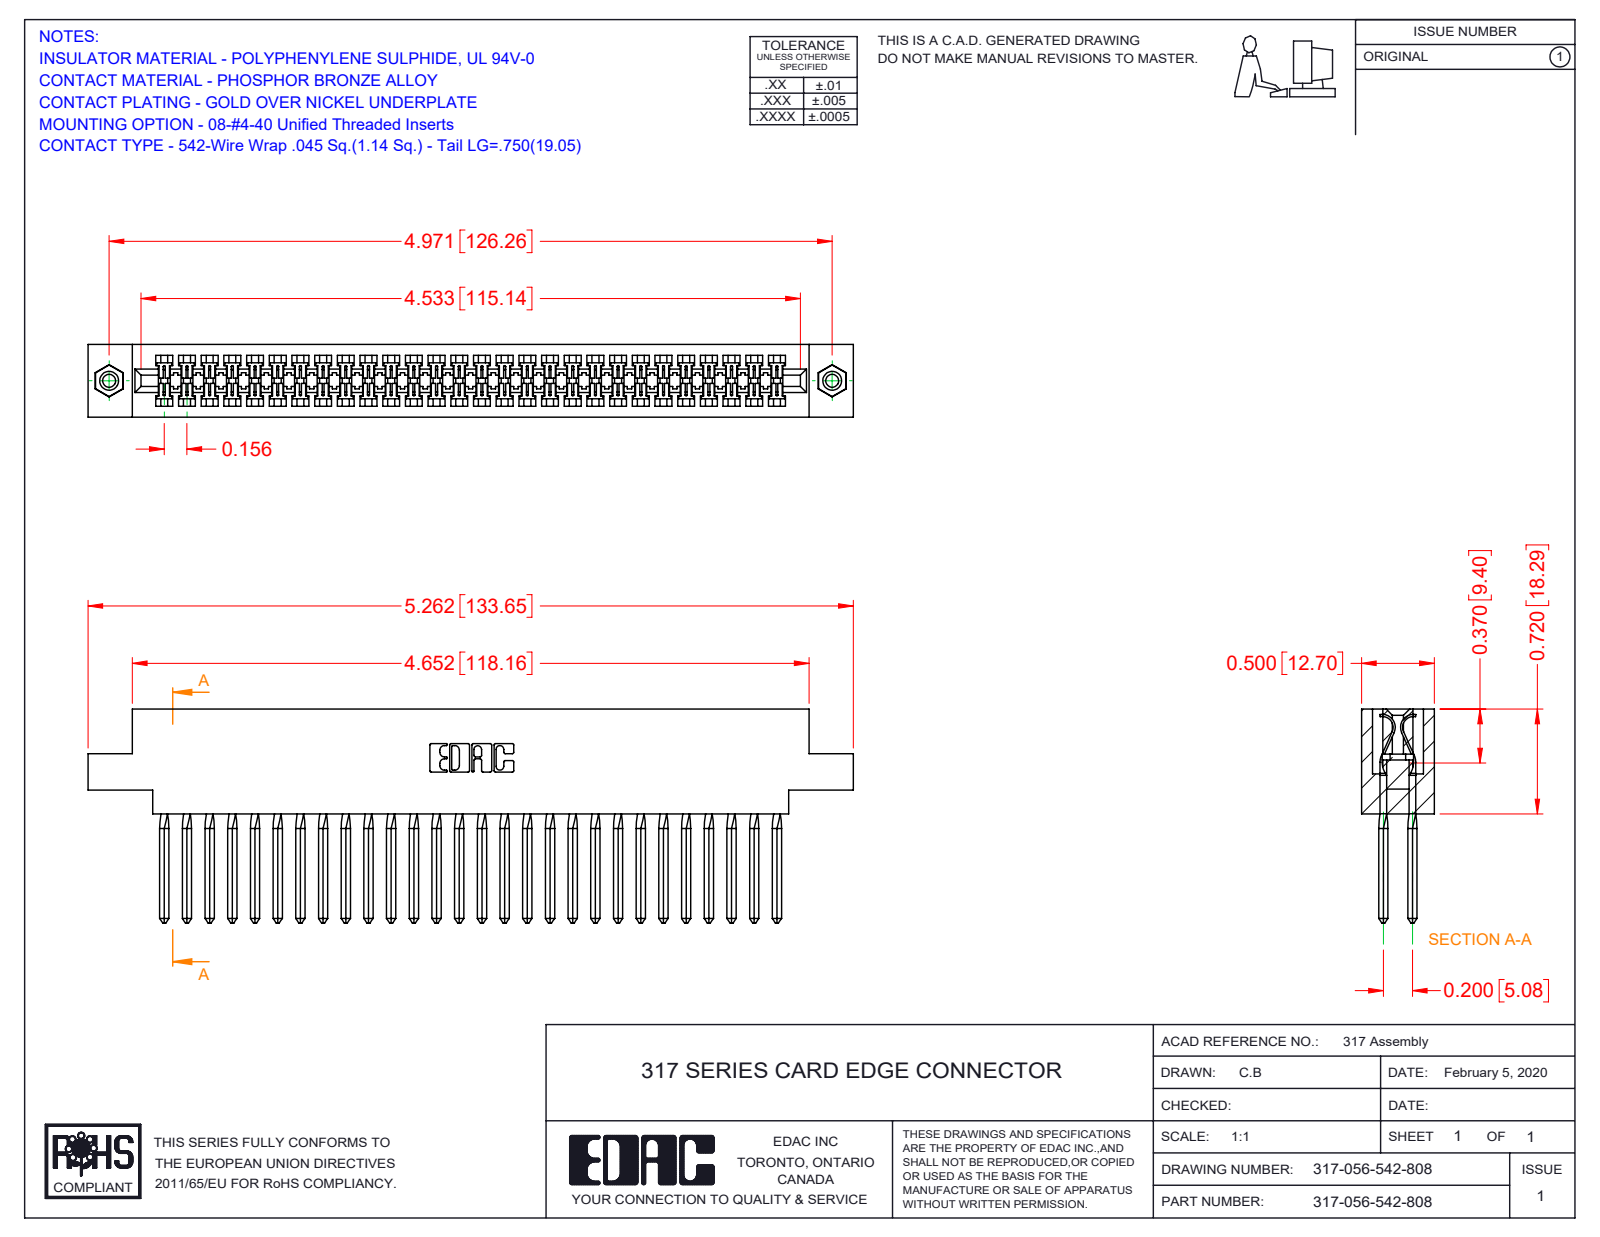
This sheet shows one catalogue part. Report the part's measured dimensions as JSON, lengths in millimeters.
{"part_name": "317-056-542-878; 345-250-001_345-250-003-102; 317 Part_.156 Dia - TI; 317-290-003_542", "step_written_by": "SolidWorks 2016 (CONFIG_CONTROL_DESIGN)", "units": "millimeters", "bodies": {"solids": 59, "faces": 3354, "planar": 2666, "cylindrical": 448, "other": 240}, "overall_size": [133.7, 37.3, 12.7], "volume_mm3": 21430, "surface_area_mm2": 29380, "round_holes": [[2.3, 2], [3.2, 2], [4, 2]], "round_bosses_or_shafts": [[3.9, 2]], "partial_cylinders_radius": [[0.2, 112], [0.3, 22], [0.2, 6], [0.8, 6], [0.7, 3], [1.9, 2], [2.3, 2], [2.5, 2]], "face_to_face_distances": [12.7, 1.9, 10.8, 8.9, 5.1, 2.8, 2.9, 1.2, 3.5, 3.3], "hole_center_spacings": [126.3]}
